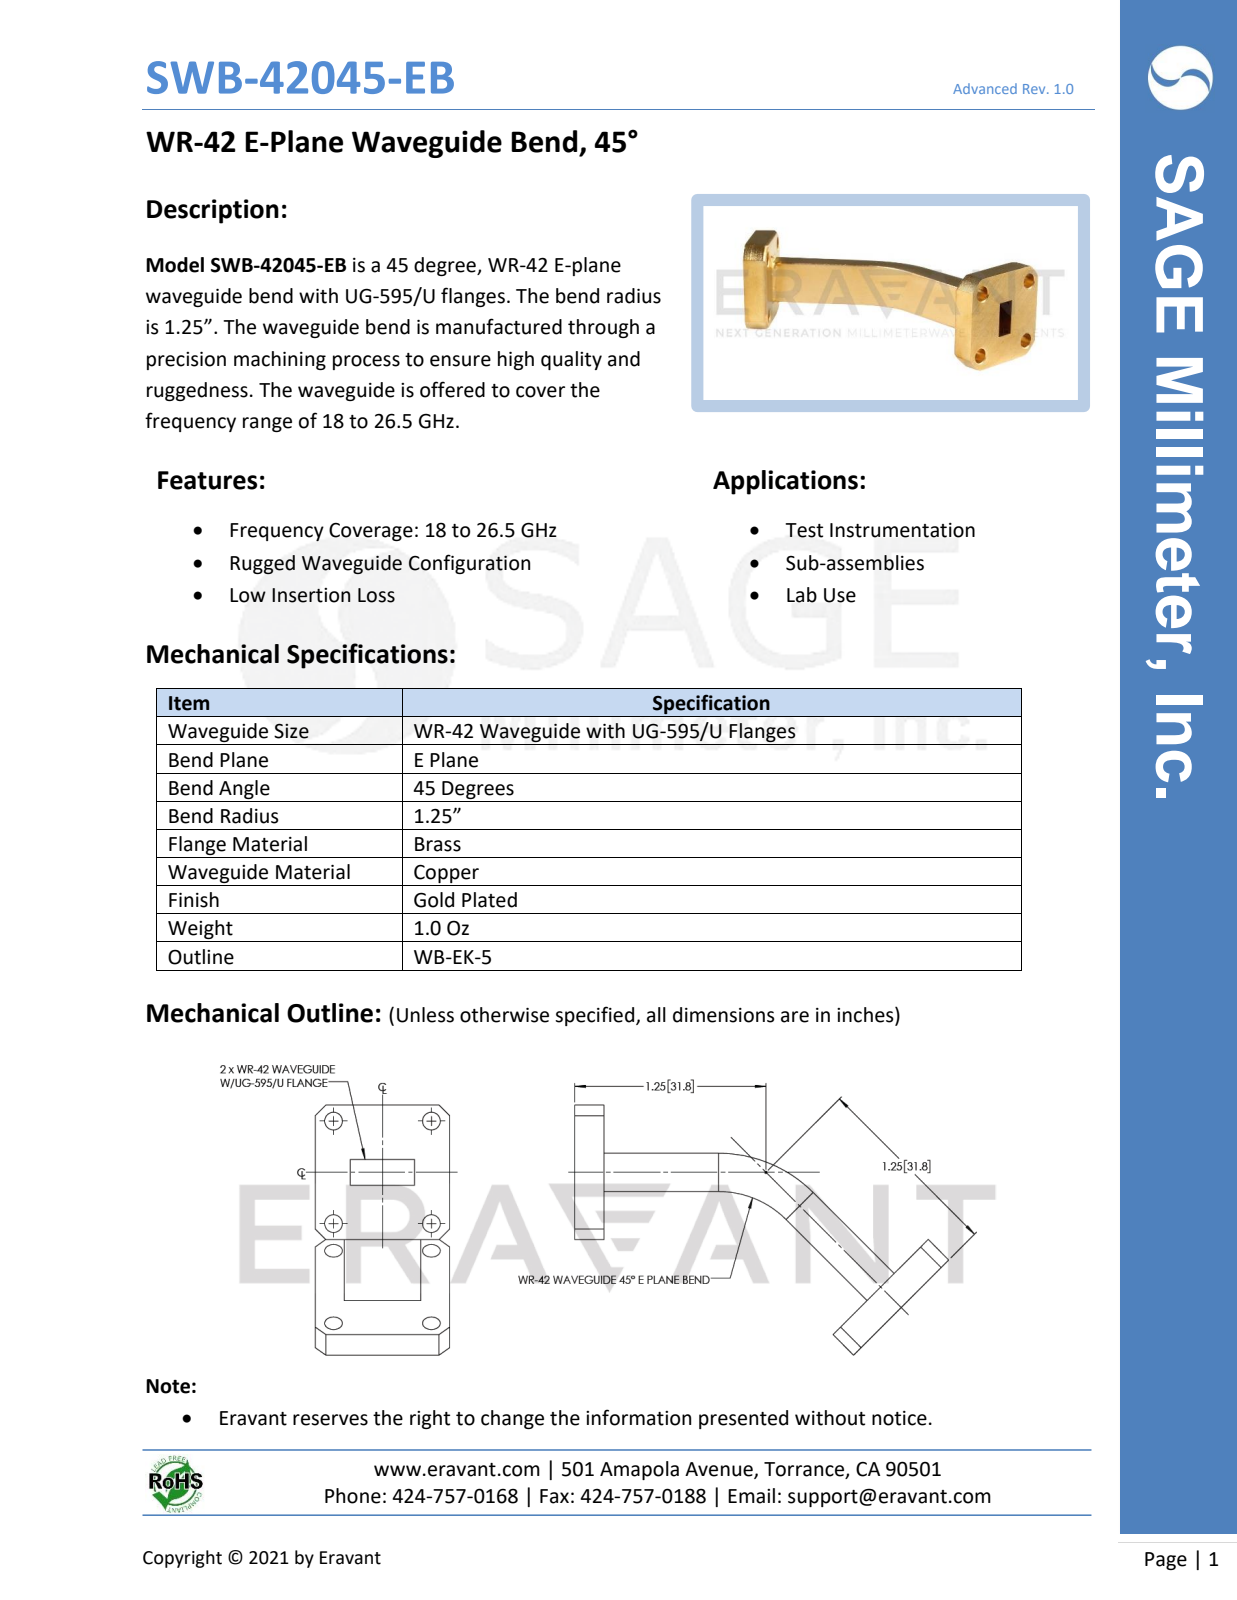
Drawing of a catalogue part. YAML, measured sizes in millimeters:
part_name: "WB-EK-5, Defeatured"
step_written_by: "SolidWorks 2021 (AUTOMOTIVE_DESIGN)"
units: millimeters
bodies: {solids: 1, faces: 60, planar: 40, cylindrical: 20, other: 0}
overall_size: [62.1, 41.5, 22.4]
volume: 5880
surface_area: 6690
round_holes:
  - {diameter: 2.9, count: 8}
partial_cylinders:
  - {radius: 15.9, count: 1}
  - {radius: 16.9, count: 1}
  - {radius: 21.2, count: 1}
  - {radius: 22.2, count: 1}
face_to_face_distances: [1, 4.8, 11.7, 4.3, 1, 5.3, 6.4, 5.3, 4.8, 5.8]
hole_center_spacings: [16.3, 17, 17, 23.5, 23.5]
